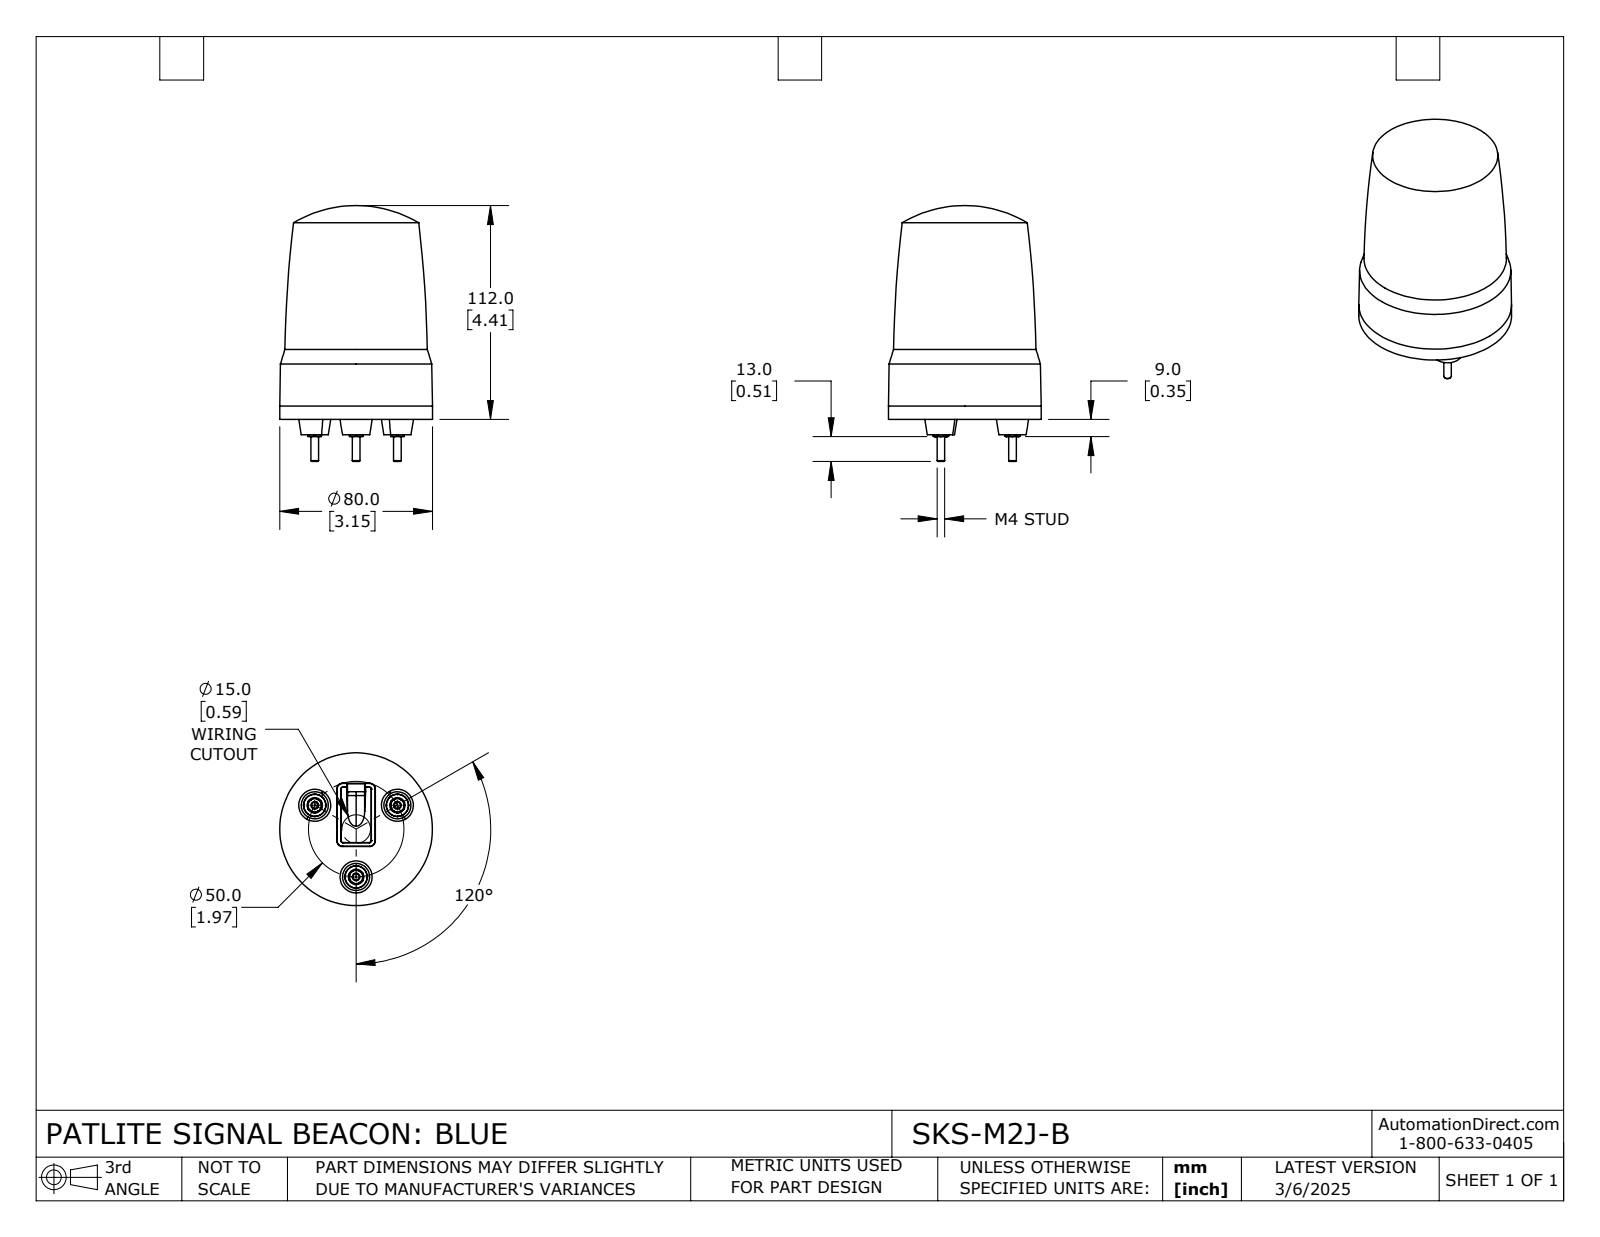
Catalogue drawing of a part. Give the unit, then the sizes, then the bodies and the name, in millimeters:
Units: millimetres
Overall size (bounding box): 134 × 80 × 80
Round bosses / shafts (diameter × count): ⌀8 ×3, ⌀4 ×3, ⌀80 ×1
Main face-to-face distances: 0.85, 2.45, 1.6, 5.3, 6.15, 7.75, 2.7, 8, 8.85, 10.45
Volume: 463 225 mm³ · Surface area: 35 408 mm²
Bodies: 1 solid, 138 faces (47 planar, 14 cylindrical, 77 other)
Part name (STEP PRODUCT): SKS-M2J-B
STEP written by: SolidWorks 2024 (CONFIG_CONTROL_DESIGN)
